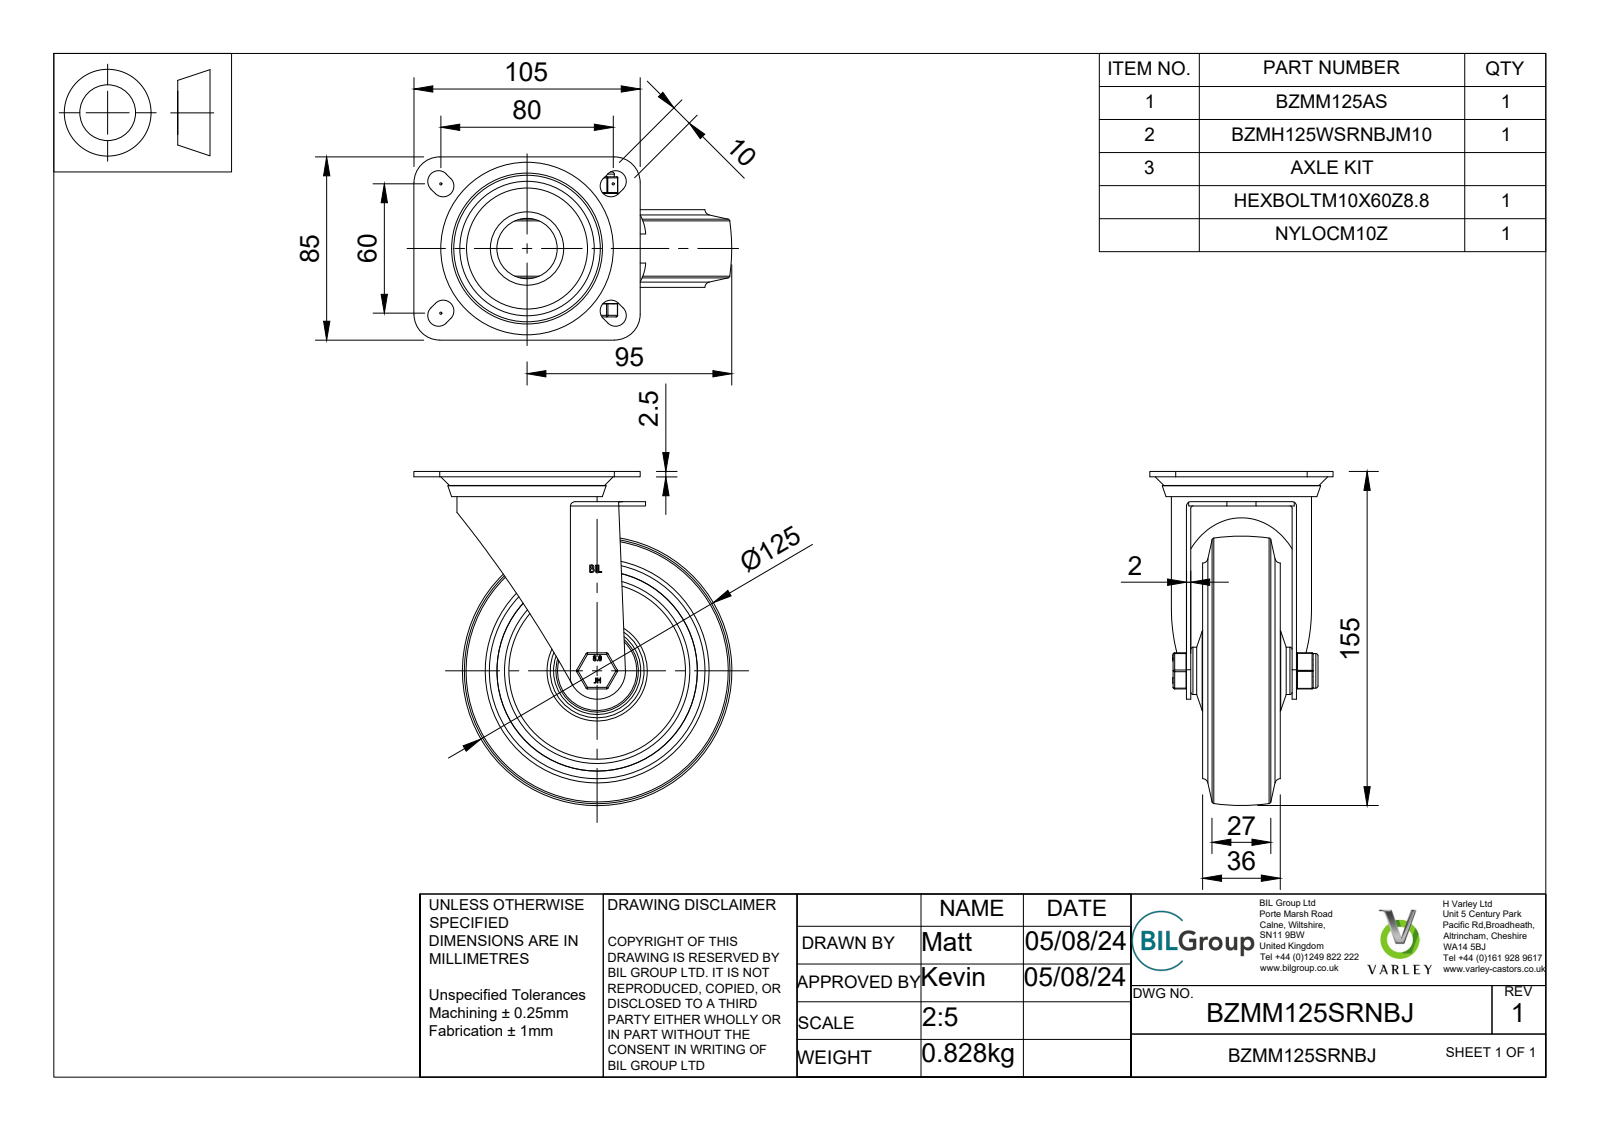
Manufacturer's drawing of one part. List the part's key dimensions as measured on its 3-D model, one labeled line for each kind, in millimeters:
Part name (STEP PRODUCT): BZMM125SRNBJ v3; BZMM125AS - 2 - 47 v1; ZINC PLATED, PRESSED STEEL TOP PLATE; ZINC PLATED, PRESSED STEEL FORKS (+8 more)
STEP written by: Autodesk Translation Framework v13.14.0.145 (AUTOMOTIVE_DESIGN)
Units: millimetres
Bodies: 23 solids, 737 faces (277 planar, 179 cylindrical, 281 other)
Overall size (bounding box): 155 × 147.5 × 85
Volume: 324 017 mm³ · Surface area: 150 207 mm²
Round holes (diameter × count): ⌀10 ×1, ⌀10.2 ×1, ⌀10.3 ×1, ⌀12 ×1, ⌀15 ×1, ⌀20 ×1, ⌀22.5 ×1, ⌀25 ×1, ⌀28 ×1, ⌀30 ×1, ⌀31 ×1, ⌀32 ×1
Round bosses / shafts (diameter × count): ⌀65 ×1, ⌀49 ×1, ⌀43.5 ×1, ⌀38.25 ×1, ⌀34.5 ×1, ⌀34 ×1, ⌀30.5 ×1, ⌀27.75 ×1
Partial cylindrical surfaces — rounded edges, fillets, slot ends (radius × count): R0.5 ×18, R0.75 ×12, R5 ×8, R12 ×5, R1 ×4, R2 ×2, R20.69 ×2, R13.14 ×1
Main face-to-face distances: 2, 7.5, 4, 16, 23.5, 20, 21.5, 2.5, 5.5, 5
